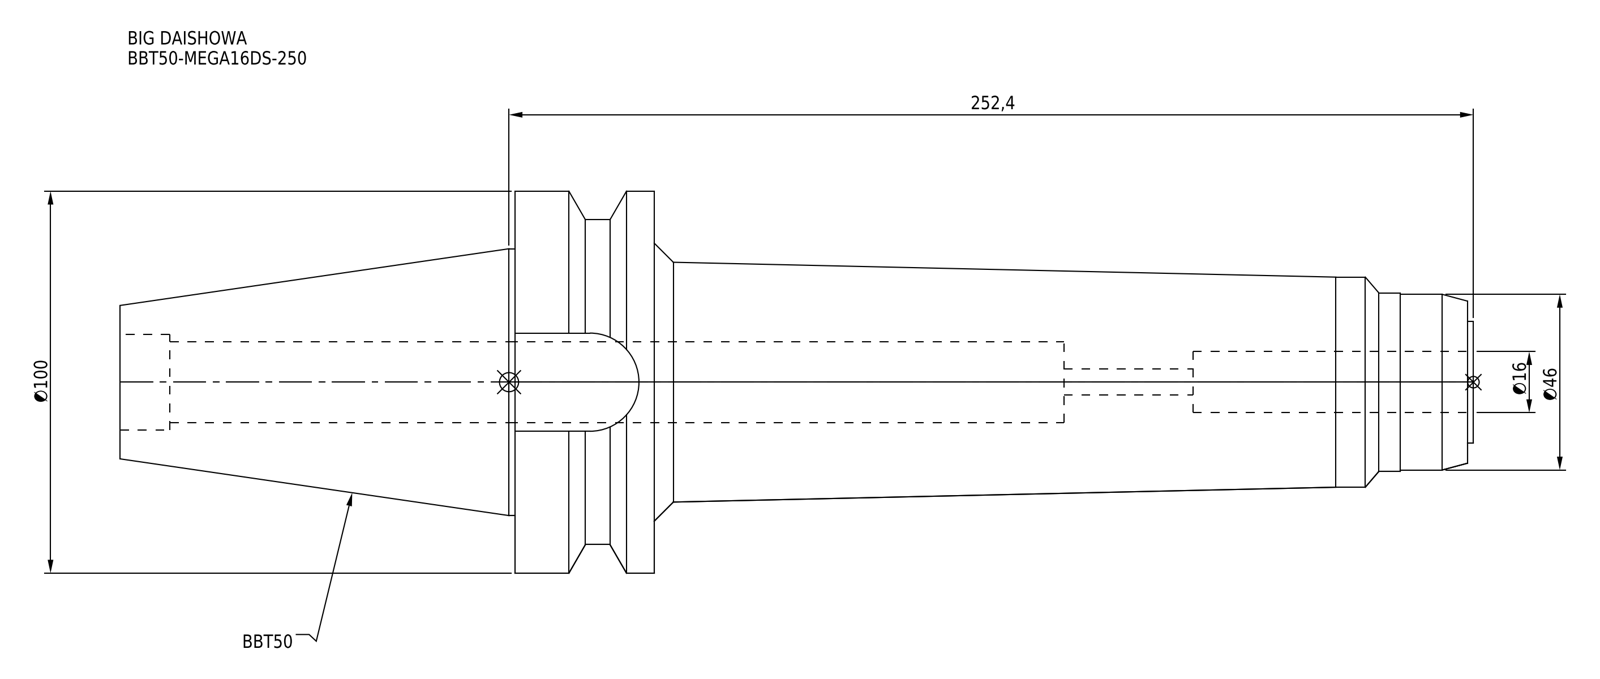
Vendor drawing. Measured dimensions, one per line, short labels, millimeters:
name: BBT50-MEGA16DS-250
written by: CREO PARAMETRIC BY PTC INC, 2016380 (AUTOMOTIVE_DESIGN)
unit: mm
bodies: 1 solid, 57 faces (15 planar, 28 cylindrical, 14 other)
size: 354.2 × 100 × 100
volume: 949 785 mm³; area: 102 917 mm²
holes: 1× ⌀6.8, 1× ⌀16, 1× ⌀21.2, 1× ⌀25
bosses: 1× ⌀100, 1× ⌀85, 1× ⌀69.85, 1× ⌀55, 1× ⌀46.7, 1× ⌀46, 1× ⌀31.9
rounds: 1× R12.85
face distances: 36.5, 139.8, 103.3, 70.8, 107.2, 212.8, 249.3, 352.6, 1.6, 214.4
